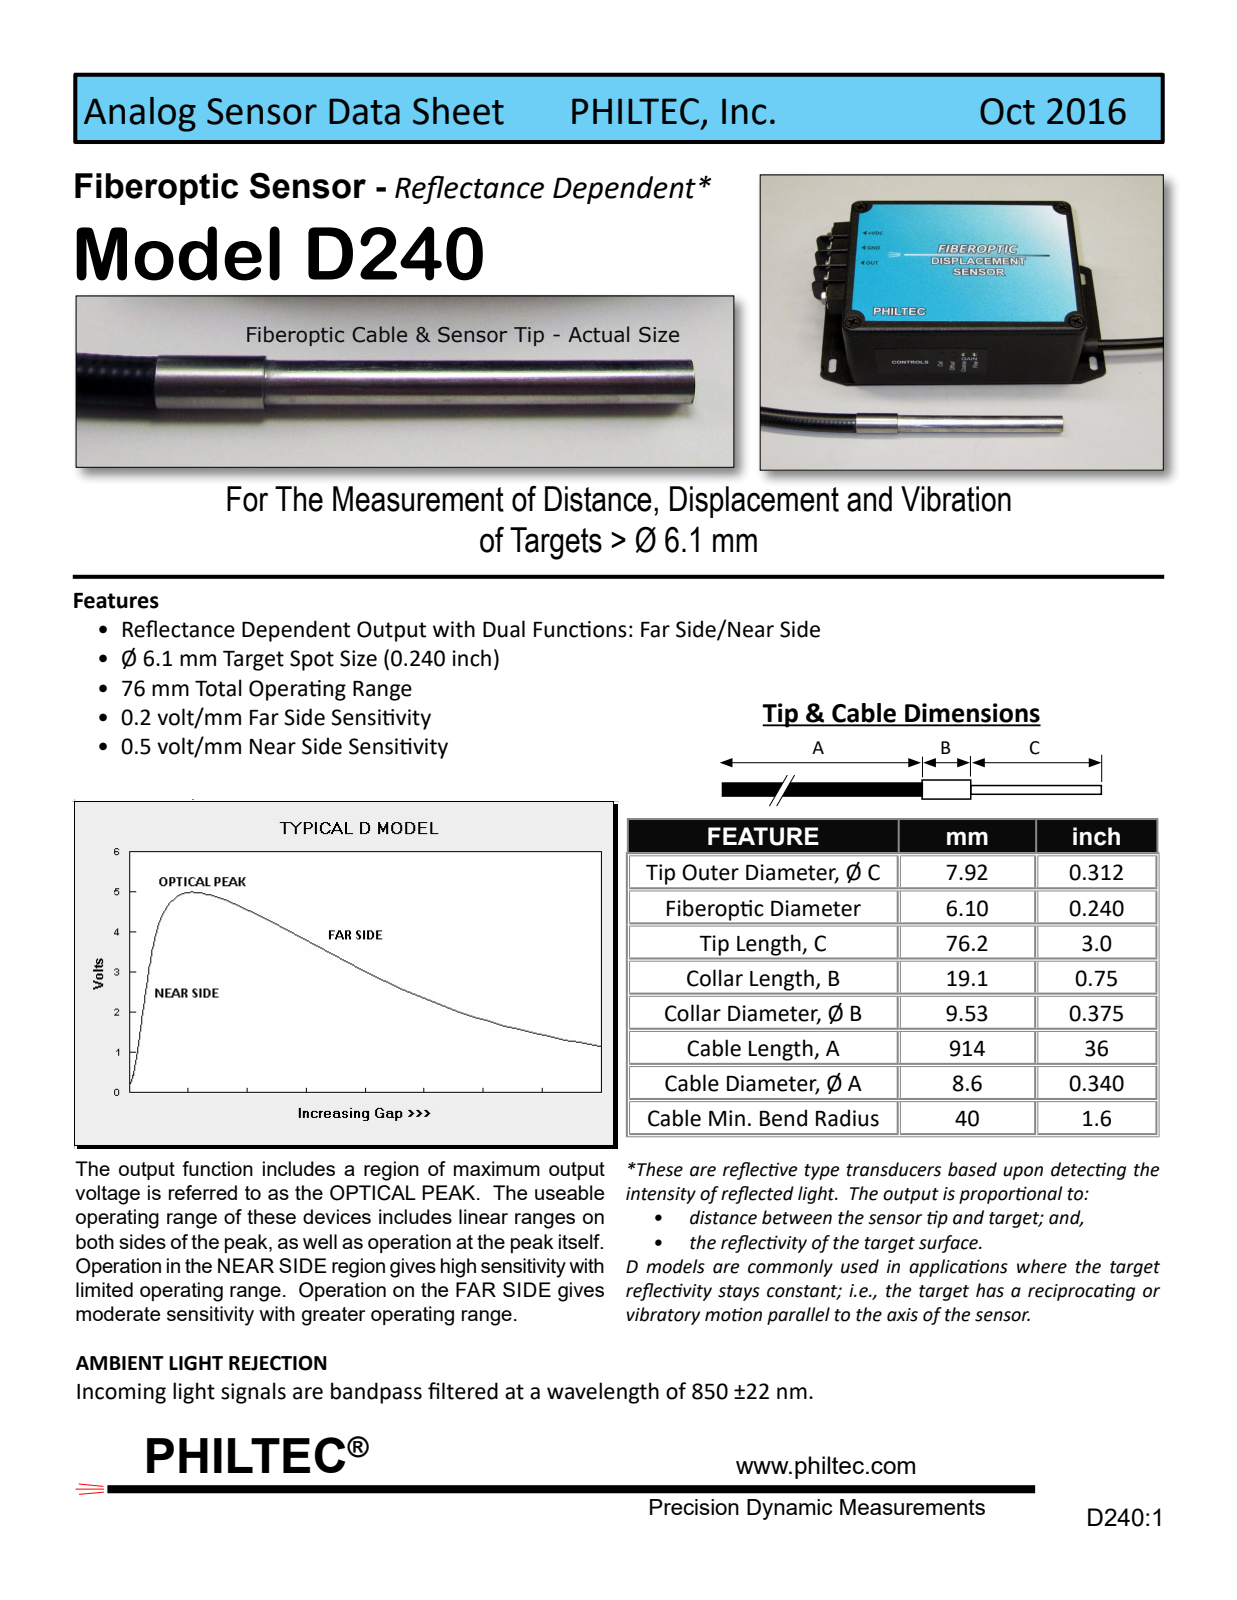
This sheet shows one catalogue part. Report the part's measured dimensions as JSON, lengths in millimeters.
{"part_name": "D Sensors", "step_written_by": "SolidWorks 2018 (CONFIG_CONTROL_DESIGN)", "units": "millimeters", "bodies": {"solids": 1, "faces": 21, "planar": 5, "cylindrical": 12, "other": 4}, "overall_size": [261.8, 96.7, 9.5], "volume_mm3": 17960, "surface_area_mm2": 8561, "round_bosses_or_shafts": [[8.6, 3], [9.5, 1], [7.9, 1], [6.1, 1]], "face_to_face_distances": [261.8, 185.6, 76.2, 166.5, 19.1, 95.3]}
